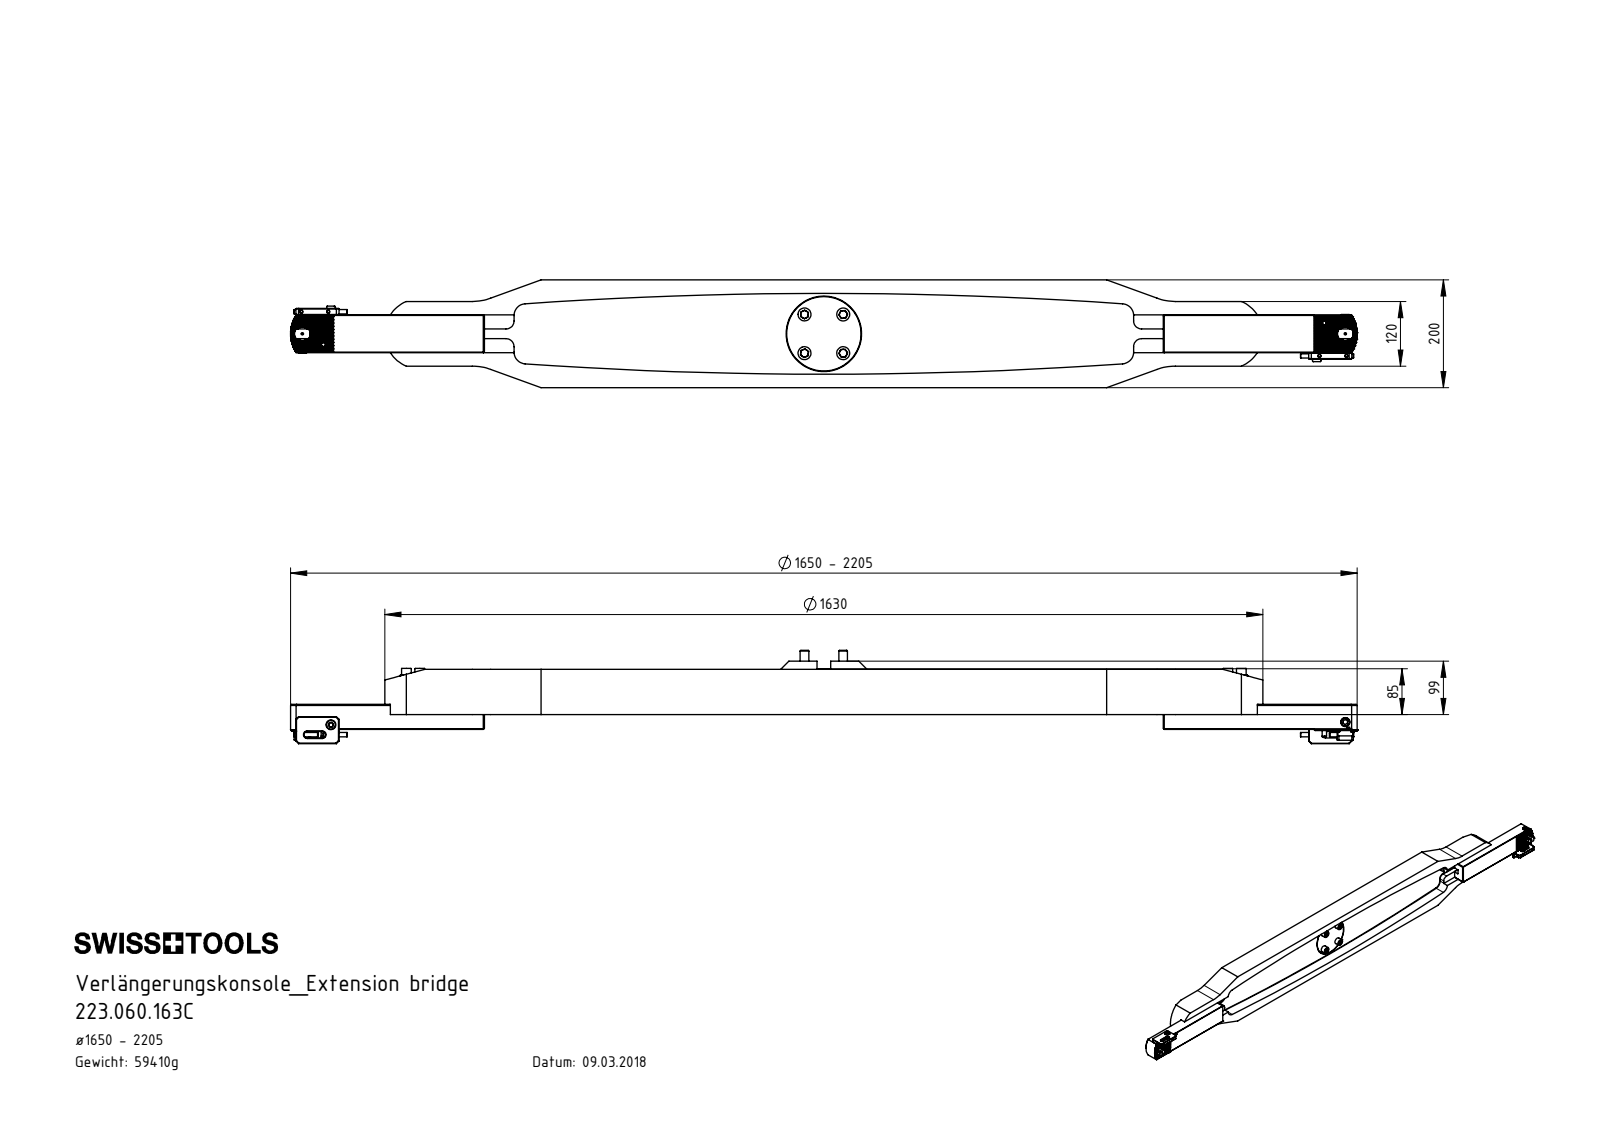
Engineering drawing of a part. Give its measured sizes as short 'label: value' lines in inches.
name: 223.060.163C; VK3-VK1.360.048; ISO 4026 - M8 x 45; VK1-ER7.001.012_A (+8 more)
written by: SolidWorks 2017 (CONFIG_CONTROL_DESIGN)
unit: in
bodies: 46 solids, 2145 faces (916 planar, 736 cylindrical, 493 other)
size: 77.953 × 7.874 × 6.811
volume: 1 042 in³; area: 2 320 in²
holes: 42× ⌀0.709, 40× ⌀0.402, 16× ⌀0.512, 4× ⌀0.197, 4× ⌀0.236, 4× ⌀0.268, 4× ⌀0.472, 4× ⌀0.669, 2× ⌀0.079, 2× ⌀0.315, 2× ⌀0.335, 2× ⌀0.413
bosses: 12× ⌀0.945, 8× ⌀0.63, 4× ⌀0.472, 2× ⌀0.394, 2× ⌀0.315, 1× ⌀5.433
rounds: 33× R0.006, 22× R0.079, 12× R0.866, 6× R0.591, 4× R0.059, 4× R0.217, 4× R0.236, 4× R0.315
face distances: 1.26, 2.559, 0.512, 1.772, 2.795, 3.307, 1.535, 7.874, 1.575, 5.315
hole spacings: 0.984, 1.857, 1.969, 2.521, 1.575, 2.953, 3.346, 57.087
